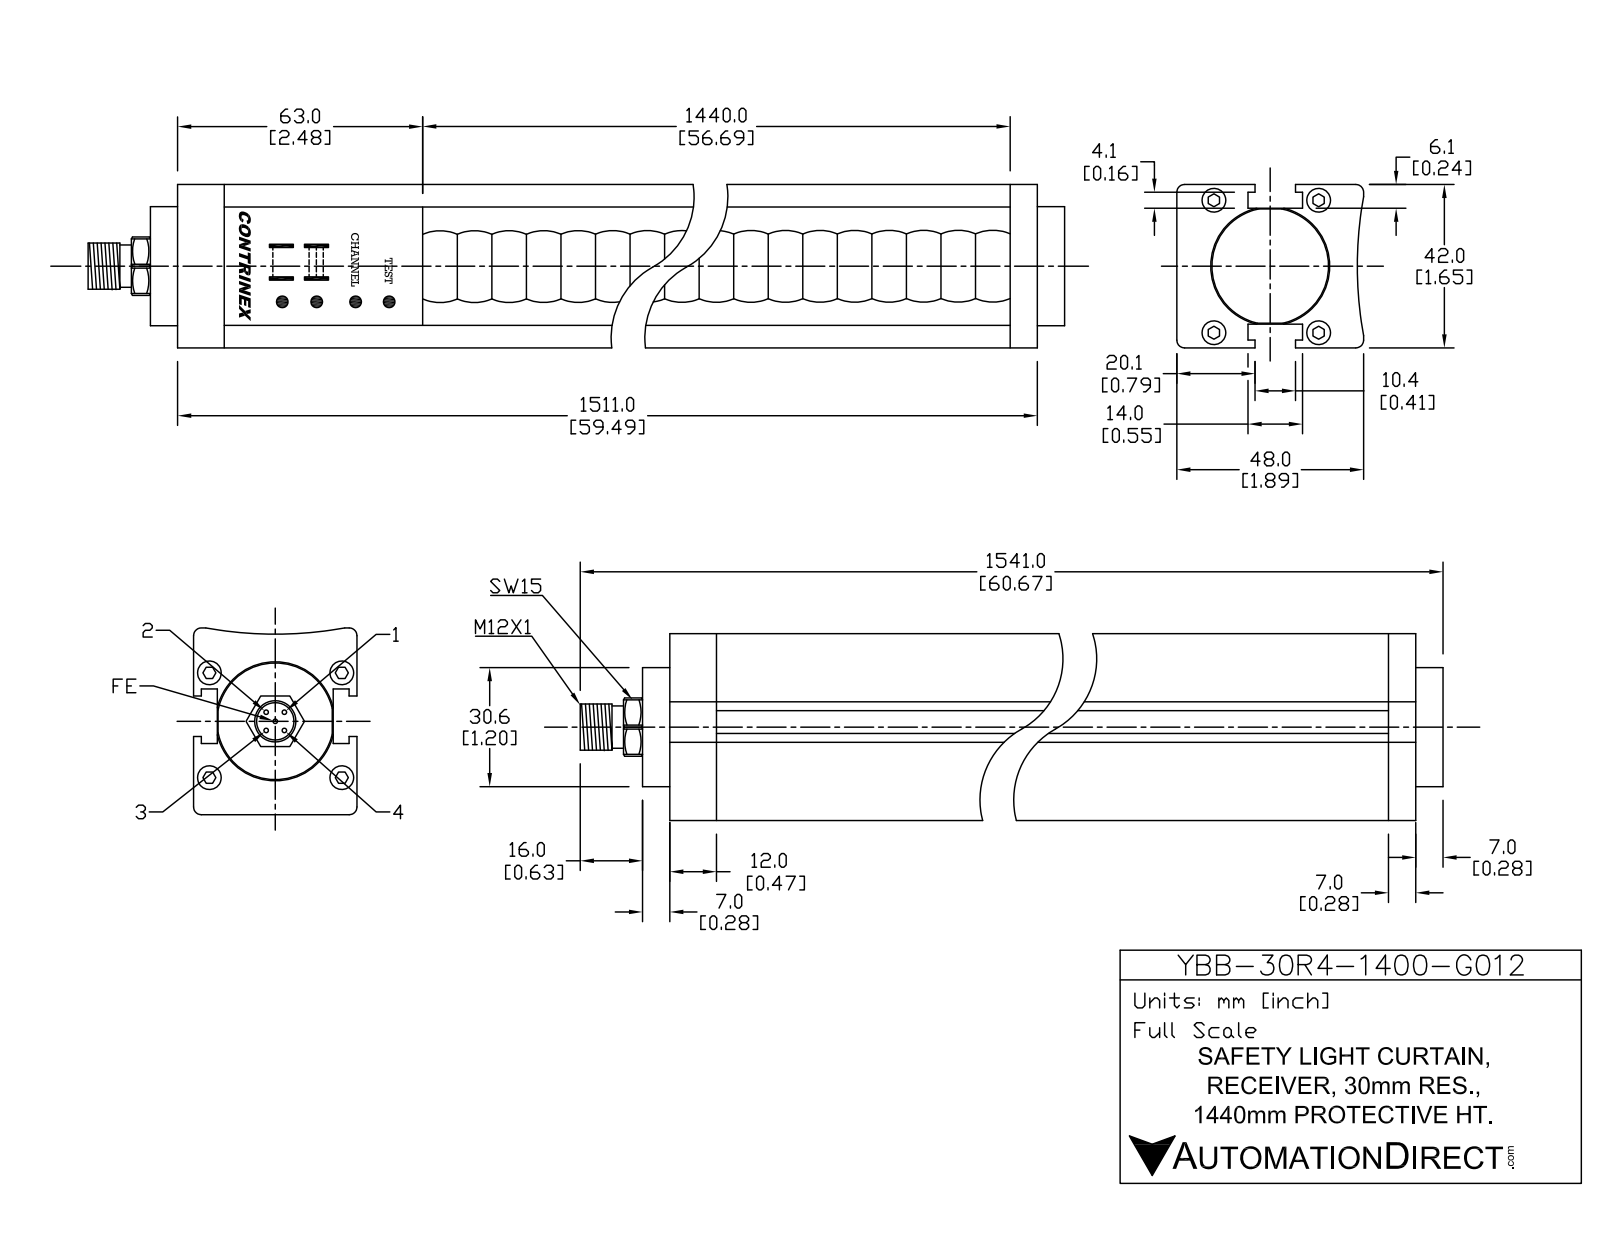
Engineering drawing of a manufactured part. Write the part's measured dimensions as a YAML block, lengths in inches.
part_name: "YBB-30R4-1400-G012"
step_written_by: "SolidWorks 2016 (AUTOMOTIVE_DESIGN)"
units: inches
bodies: {solids: 19, faces: 440, planar: 208, cylindrical: 168, other: 64}
overall_size: [60.669, 1.89, 1.654]
volume: 165.7
surface_area: 526.7
round_holes:
  - {diameter: 0.236, count: 4}
  - {diameter: 0.335, count: 1}
  - {diameter: 1.26, count: 1}
round_bosses_or_shafts:
  - {diameter: 0.039, count: 5}
  - {diameter: 0.217, count: 4}
  - {diameter: 1.205, count: 1}
  - {diameter: 0.472, count: 1}
  - {diameter: 0.413, count: 1}
partial_cylinders:
  - {radius: 0.039, count: 48}
  - {radius: 0.02, count: 4}
  - {radius: 0.022, count: 2}
  - {radius: 0.323, count: 1}
  - {radius: 3.937, count: 1}
face_to_face_distances: [0.248, 1.406, 1.654, 1.157, 0.551, 0.677, 1.228, 0.618, 1.169, 1.846]
hole_center_spacings: [0.828, 0.88, 1.059, 1.339, 1.707]
